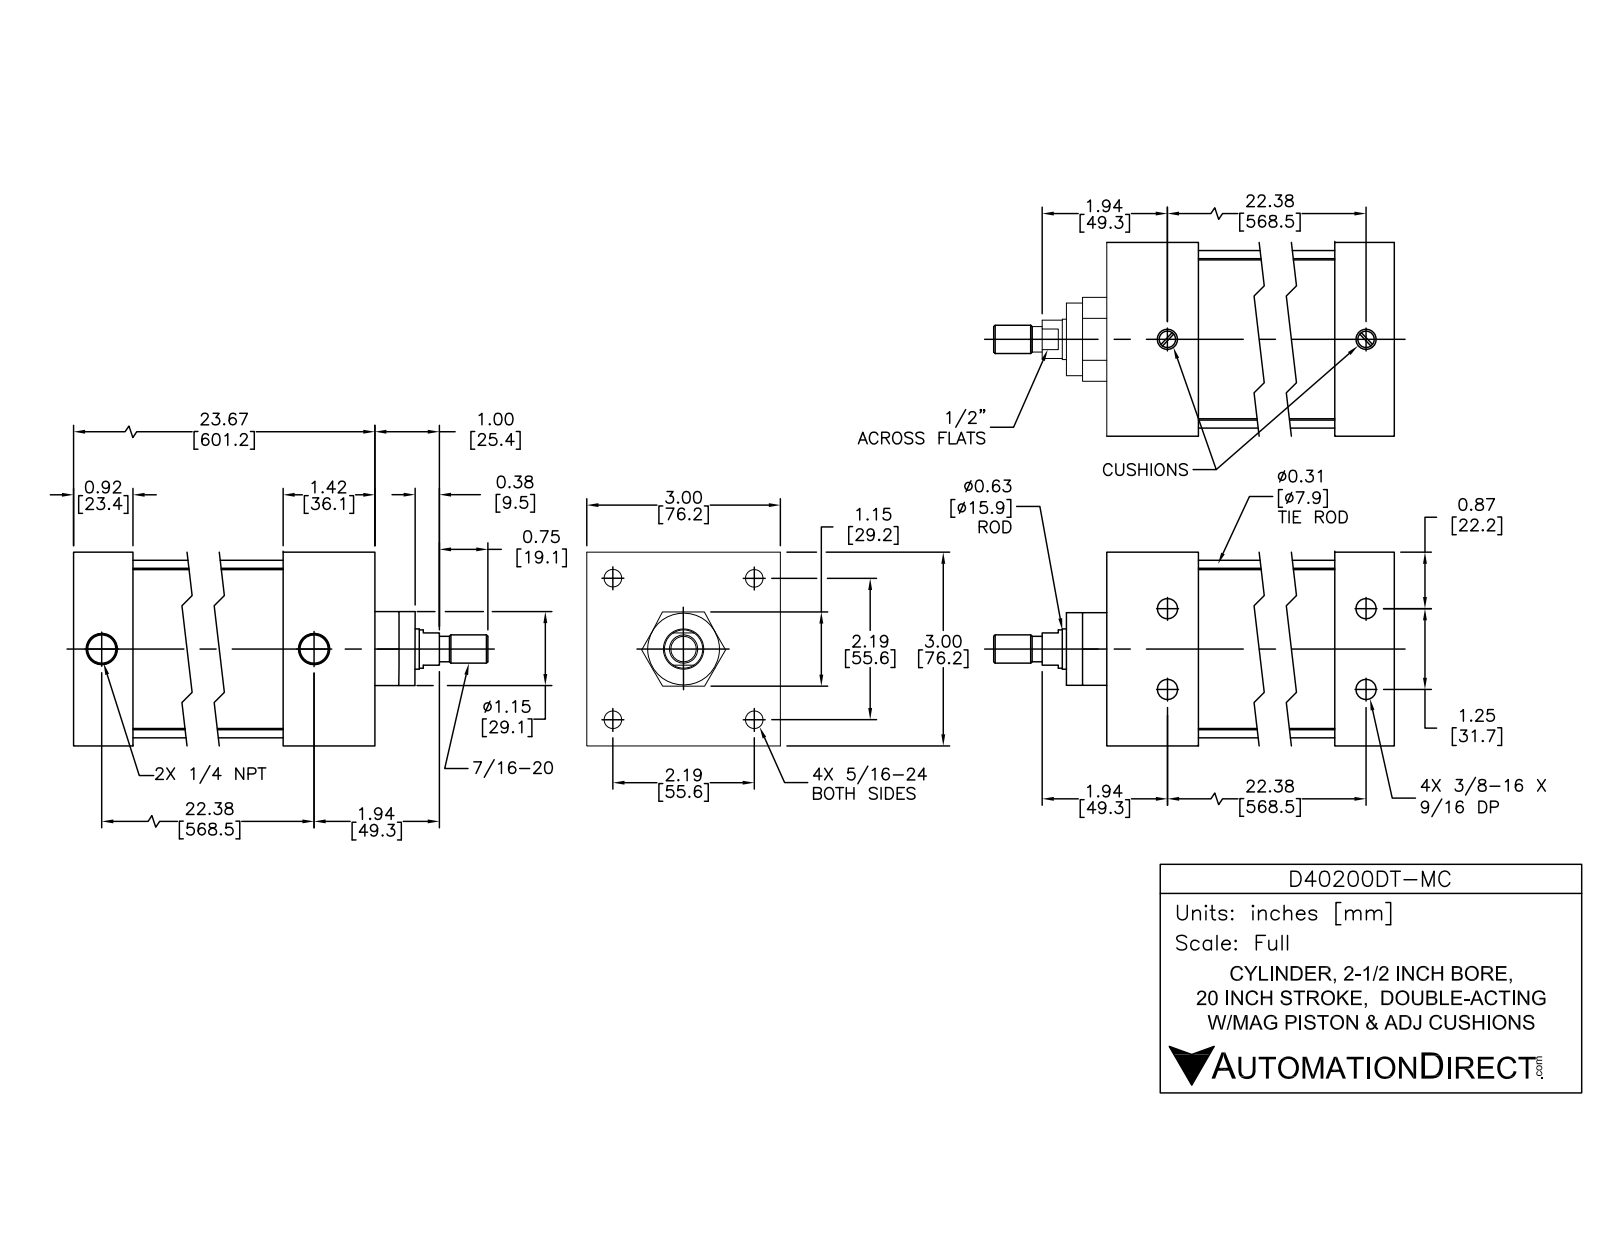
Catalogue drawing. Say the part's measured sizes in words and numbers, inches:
The part is named "D40200DT-MC; D40200DT-M PISTON; D40200DT-M BODY". Its 3-D file was written by "SolidWorks 2015 (AUTOMOTIVE_DESIGN)". It is 12 solids with 298 faces: 94 planar, 114 cylindrical and 90 other. Overall it measures 25.496 by 3 by 3 inches. Its volume is 60.9 cubic inches and its surface area 592.5 square inches. Round holes: 4 of diameter 0.267, 4 of diameter 0.307, 4 of diameter 0.359, 4 of diameter 0.5, 2 of diameter 0.297, 2 of diameter 0.477, 1 of diameter 0.625, 1 of diameter 0.628, 1 of diameter 2.5. Round bosses or shafts: 4 of diameter 0.484, 4 of diameter 0.313, 4 of diameter 0.282, 1 of diameter 2.75, 1 of diameter 2.497, 1 of diameter 1.12, 1 of diameter 0.622, 1 of diameter 0.59. Partial cylindrical surfaces (rounded edges, fillets, slot ends): 4 of radius 0.3. The main face-to-face distances are 3, 0.08, 21.326, 23.746, 22.726, 1.02, 1.42, 21.306, 22.326, 1. The hole center spacings are 1.556, 2.2, 22.379, 22.37, 0.625, 0.625, 1.25, 3.111.
